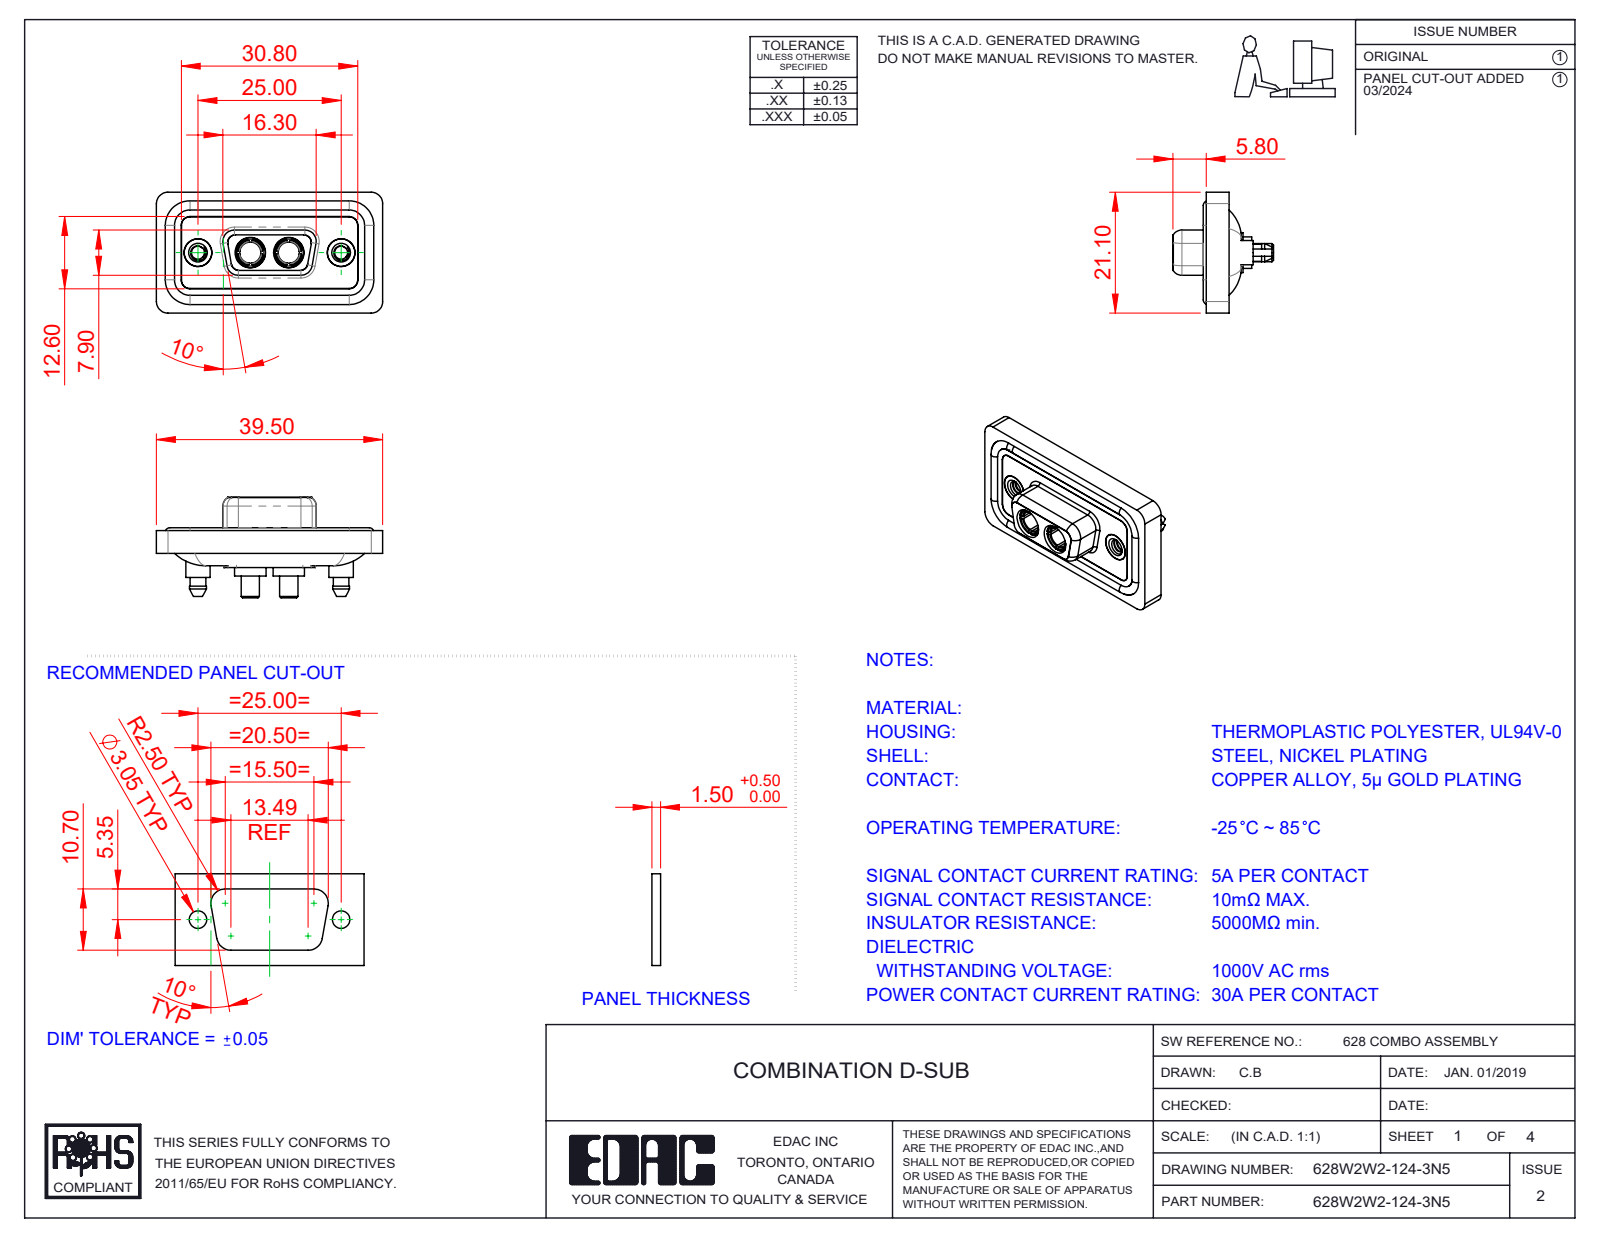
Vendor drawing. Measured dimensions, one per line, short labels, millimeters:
name: 628Combo Shell Front_09 Contacts; 628Combo Waterproof Housing_09 Contacts; 628W2W2-124-3N5; 628Combo Housing_2W2 (+3 more)
written by: SolidWorks 2023 (CONFIG_CONTROL_DESIGN)
unit: mm
bodies: 11 solids, 584 faces (179 planar, 266 cylindrical, 139 other)
size: 39.5 × 21.1 × 17.55
volume: 4 861 mm³; area: 7 978 mm²
holes: 4× ⌀4.85, 2× ⌀2.26, 2× ⌀3.7, 2× ⌀4, 2× ⌀4.05, 2× ⌀5, 2× ⌀5.3
bosses: 4× ⌀1.6, 2× ⌀5.5, 2× ⌀5.4, 2× ⌀5.2, 2× ⌀4.96, 2× ⌀4.95, 2× ⌀4.8, 2× ⌀4.75
rounds: 24× R1.5, 18× R2, 10× R1.6, 8× R1.35, 4× R0.25, 4× R0.5, 4× R0.6, 4× R0.65
face distances: 0.4, 1.8, 1.1, 2.9, 1.6, 0.5, 5.65, 7.45, 1.5, 4
hole spacings: 9.14, 15.86, 6.72, 25
